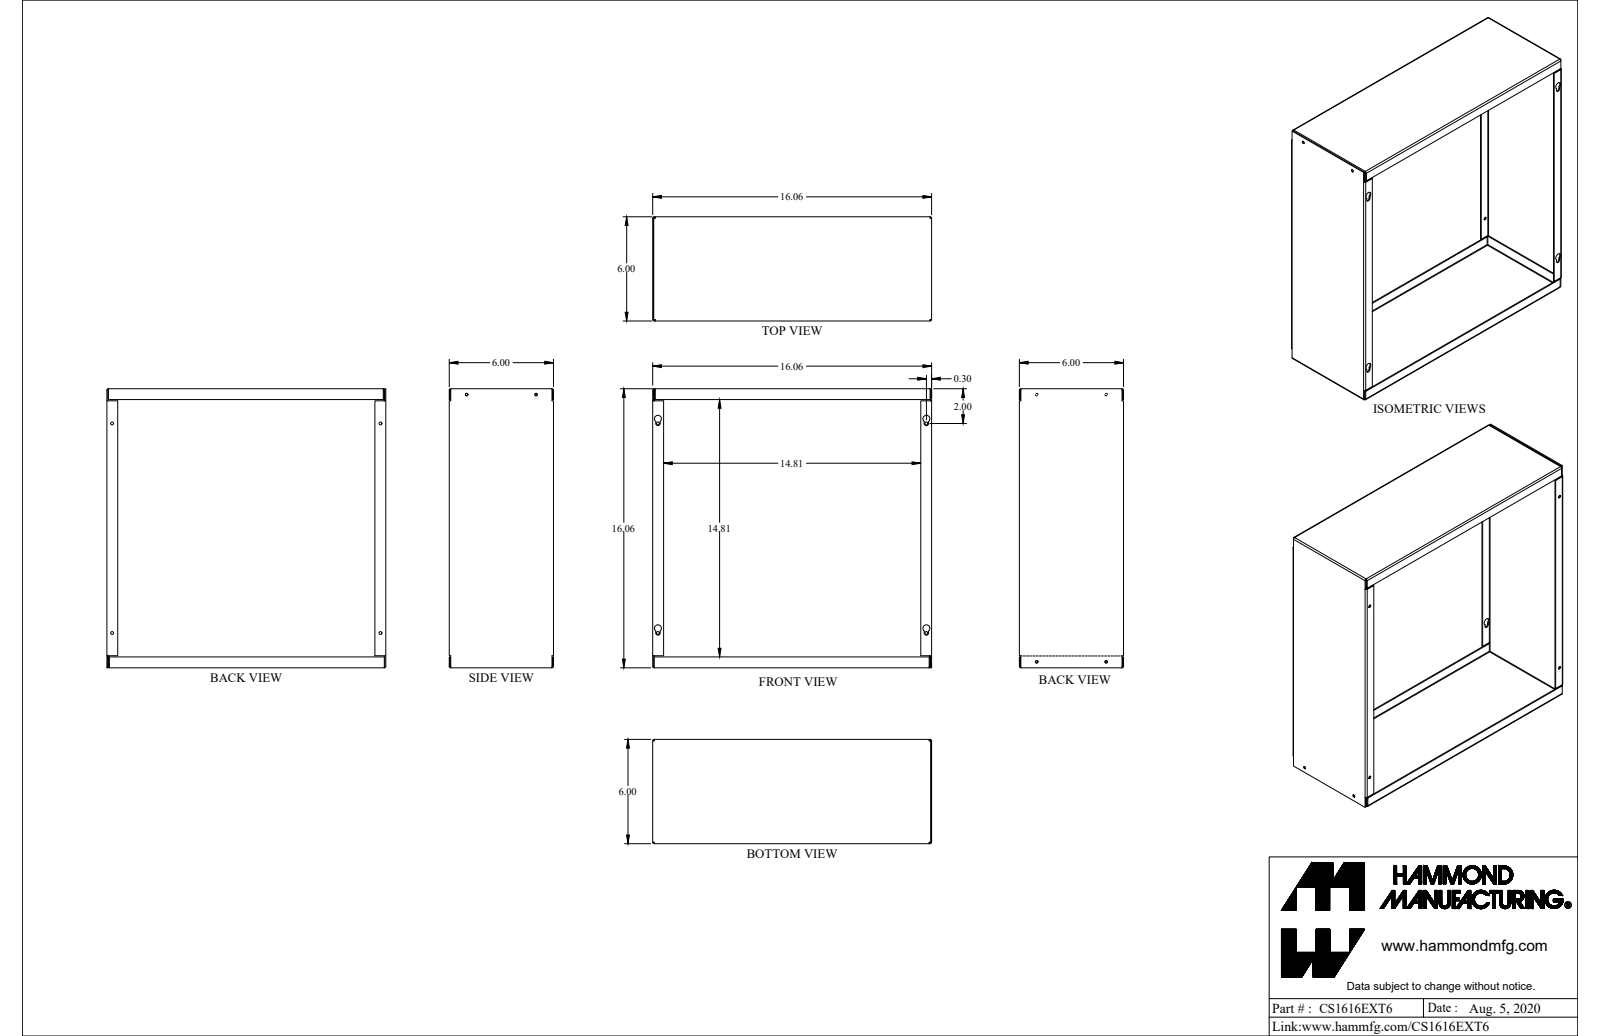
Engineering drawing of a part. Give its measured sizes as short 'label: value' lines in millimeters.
name: CS1616EXT6
written by: SolidWorks 2021 (AUTOMOTIVE_DESIGN)
unit: mm
bodies: 2 solids, 124 faces (80 planar, 44 cylindrical, 0 other)
size: 408 × 408 × 152.4
volume: 425 700 mm³; area: 594 500 mm²
holes: 4× ⌀3.7, 4× ⌀4.3
bosses: 4× ⌀3.3
rounds: 12× R0.7, 12× R2.2, 4× R3.2, 4× R5.2
face distances: 406.6, 1.4, 1.4, 405.1, 408, 408, 405.1, 151, 152.4, 149.5
hole spacings: 101.6, 306.4, 390.7, 392.7, 403.7, 498
